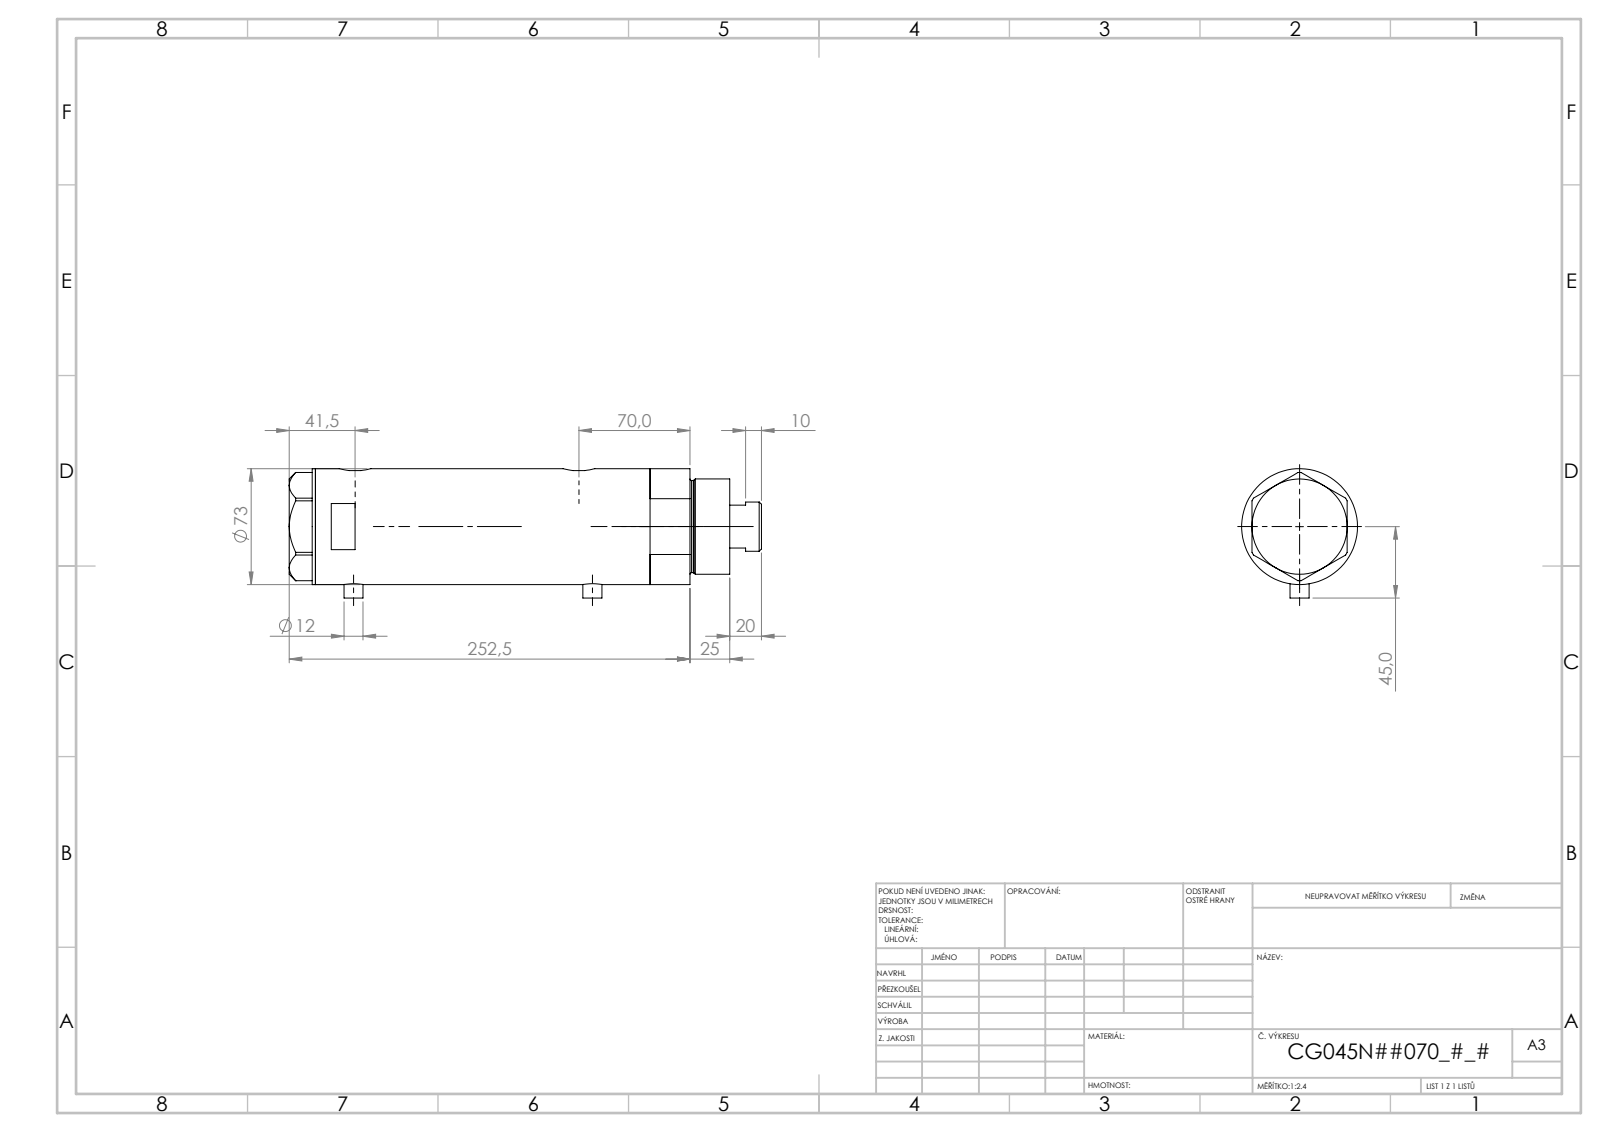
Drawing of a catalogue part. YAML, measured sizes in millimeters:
part_name: "V270CG_MIDDLE; V270CG_FRONT; V270CG_VC; V270CG_BACK"
step_written_by: "SolidWorks 2019 (CONFIG_CONTROL_DESIGN)"
units: millimeters
bodies: {solids: 4, faces: 125, planar: 50, cylindrical: 55, other: 20}
overall_size: [261.52, 74.1, 73]
volume: 904700
surface_area: 152927
round_holes:
  - {diameter: 5, count: 2}
  - {diameter: 12.5, count: 2}
  - {diameter: 13.16, count: 2}
  - {diameter: 10.5, count: 1}
  - {diameter: 32, count: 1}
  - {diameter: 33.5, count: 1}
  - {diameter: 45, count: 1}
  - {diameter: 48, count: 1}
  - {diameter: 64, count: 1}
round_bosses_or_shafts:
  - {diameter: 12, count: 2}
  - {diameter: 73, count: 1}
  - {diameter: 60, count: 1}
  - {diameter: 58, count: 1}
  - {diameter: 31, count: 1}
partial_cylinders:
  - {radius: 10, count: 2}
face_to_face_distances: [137.15, 42.5, 153.65, 111.15, 16.5, 16.51, 26, 25.99, 137.14, 225.02]
hole_center_spacings: [121.65, 0.99, 1, 8.5, 8.51, 112.15, 113.14, 113.15]
